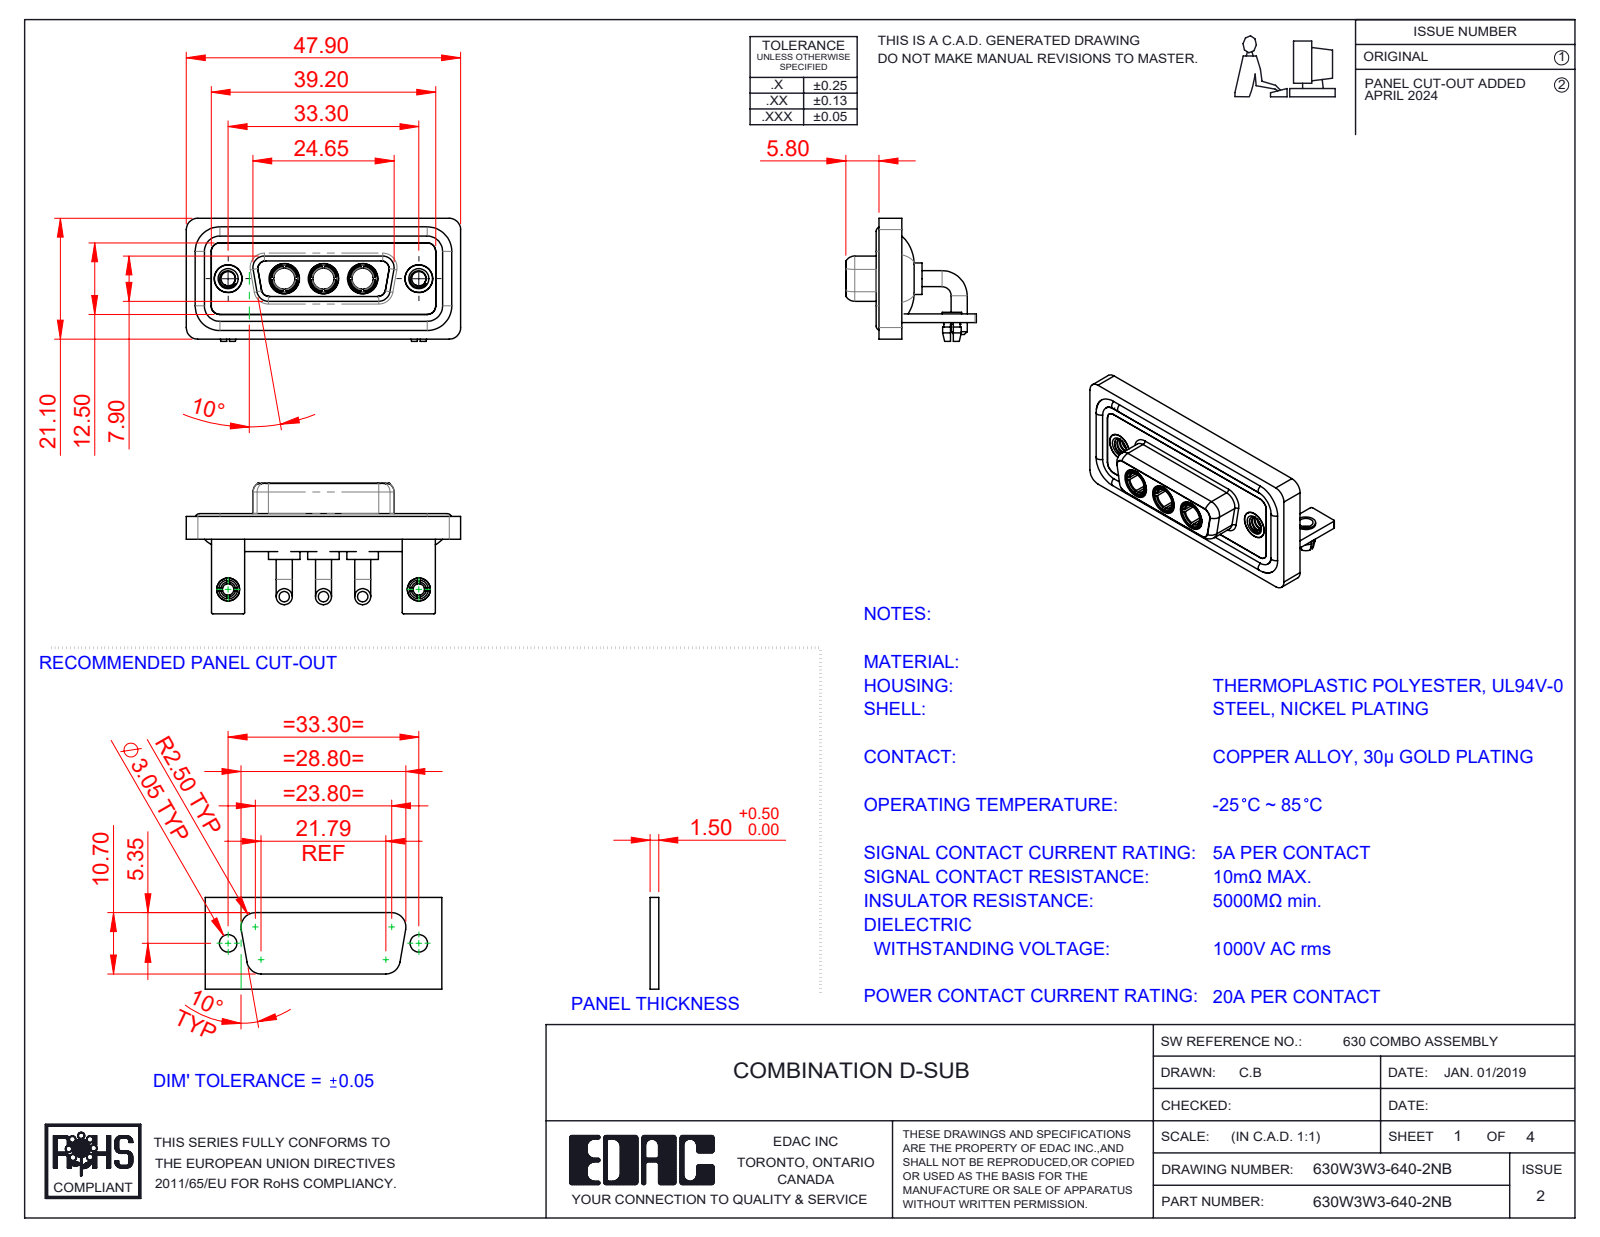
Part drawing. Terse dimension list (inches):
name: 630Combo Shell Rear_15 Contacts; 630Combo Board Lock_50 Contacts; 630Combo Threaded Rivet_A; 630Combo Stabilizer Bracket_50 Contacts (+5 more)
written by: SolidWorks 2023 (CONFIG_CONTROL_DESIGN)
unit: in
bodies: 17 solids, 754 faces (260 planar, 317 cylindrical, 177 other)
size: 1.886 × 0.898 × 0.846
volume: 0.401 in³; area: 16.93 in²
holes: 5× ⌀0.191, 4× ⌀0.098, 3× ⌀0.146, 3× ⌀0.209, 2× ⌀0.079, 2× ⌀0.126, 2× ⌀0.157, 2× ⌀0.159, 2× ⌀0.197
bosses: 6× ⌀0.11, 4× ⌀0.063, 3× ⌀0.217, 3× ⌀0.205, 3× ⌀0.195, 3× ⌀0.187, 3× ⌀0.148, 2× ⌀0.195
rounds: 21× R0.079, 18× R0.059, 16× R0.01, 12× R0.053, 8× R0.063, 5× R0.02, 4× R0.024, 4× R0.026
face distances: 0.016, 0.114, 0.059, 0.071, 0.146, 0.043, 0.161, 0.063, 0.098, 0.055
hole spacings: 0.27, 0.386, 0.656, 0.925, 1.311, 0.539
